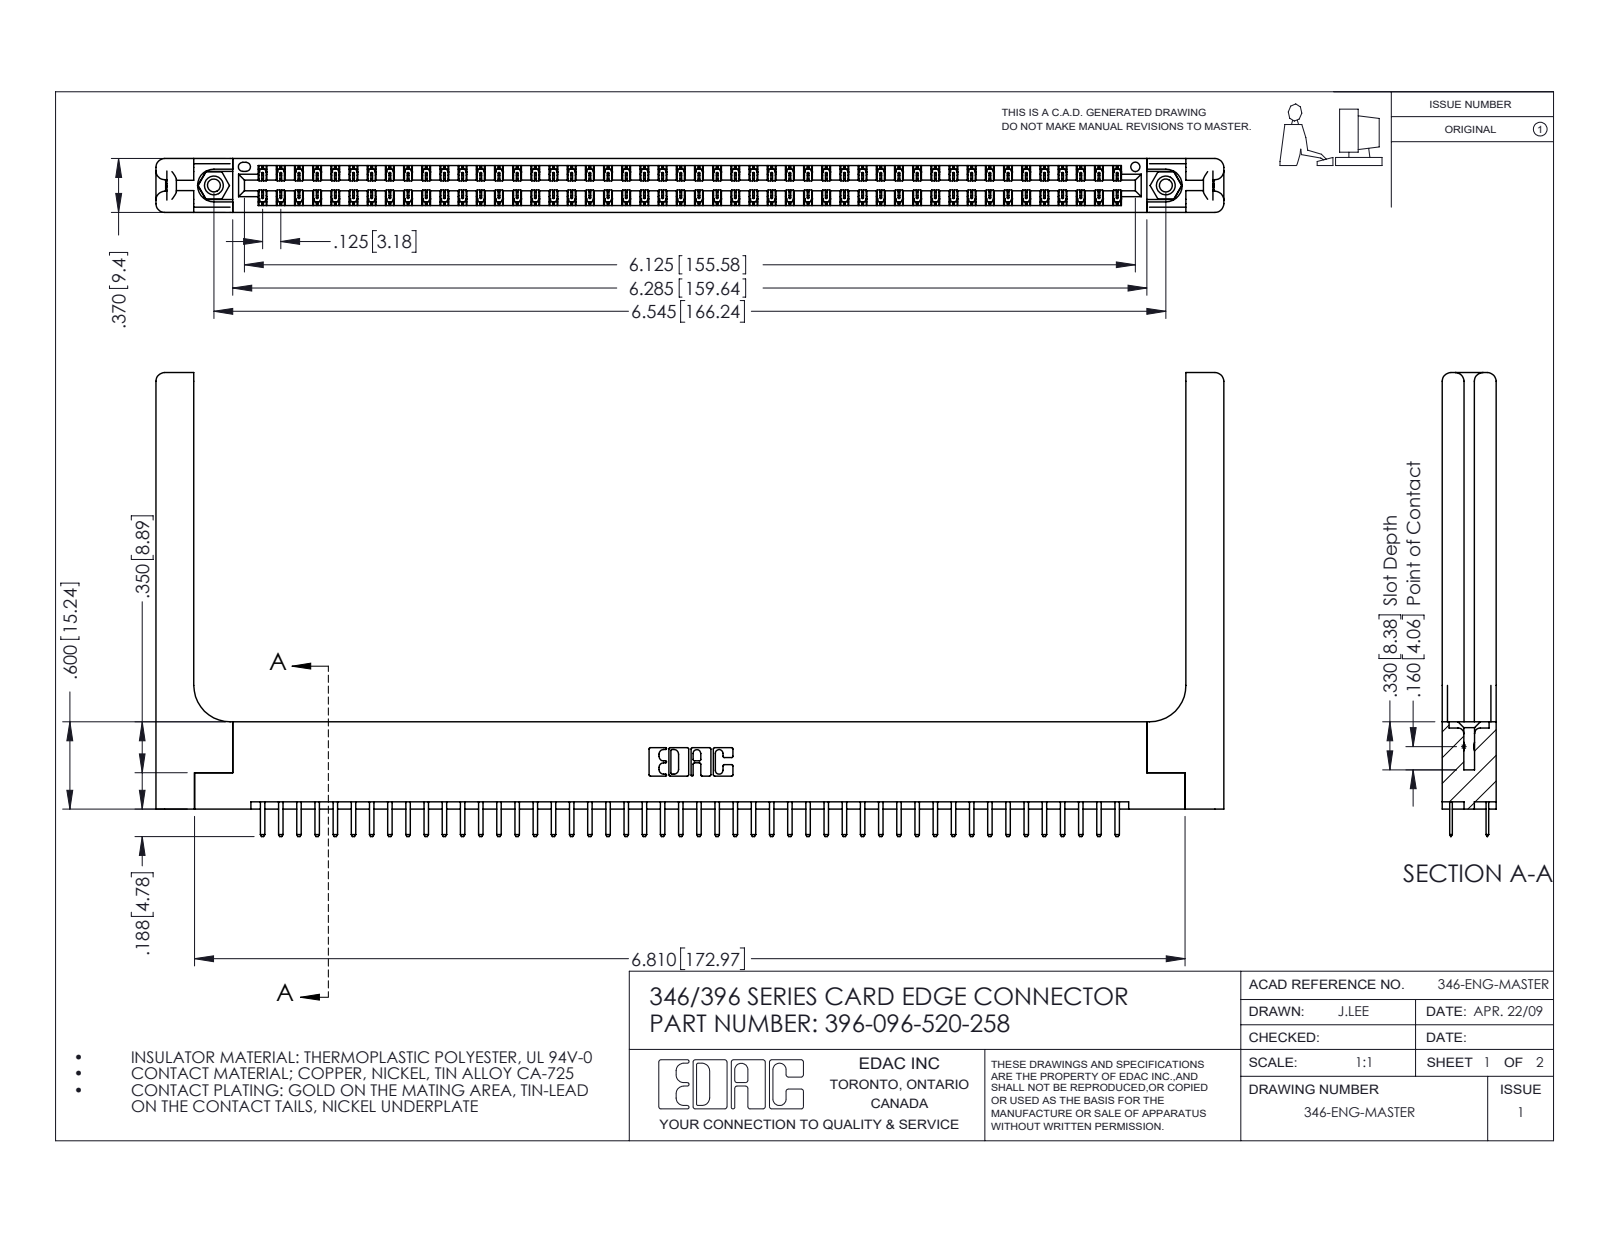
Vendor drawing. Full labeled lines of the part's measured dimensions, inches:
Part name (STEP PRODUCT): 345-250-001_345-250-001-102; 345-292-001_345-293-120; 346-220-058_345-220-058; 346 Part_Flush Mounting Lugs - 0.156 Dia-TH (+1 more)
STEP written by: SolidWorks 2016 (CONFIG_CONTROL_DESIGN)
Units: inches
Bodies: 101 solids, 5754 faces (3776 planar, 1918 cylindrical, 60 other)
Overall size (bounding box): 7.341 × 3.188 × 0.37
Volume: 1.567 in³ · Surface area: 46.45 in²
Round holes (diameter × count): ⌀0.089 ×2, ⌀0.125 ×2, ⌀0.156 ×2, ⌀0.064 ×1
Round bosses / shafts (diameter × count): ⌀0.155 ×2
Partial cylindrical surfaces — rounded edges, fillets, slot ends (radius × count): R0.006 ×144, R0.01 ×100, R0.01 ×22, R0.06 ×16, R0.007 ×6, R0.031 ×6, R0.026 ×3, R0.014 ×2
Main face-to-face distances: 0.37, 0.048, 0.322, 0.072, 0.25, 0.148, 0.15, 0.298, 0.025, 0.275
Hole centre spacings: 0.246, 6.336, 6.545
